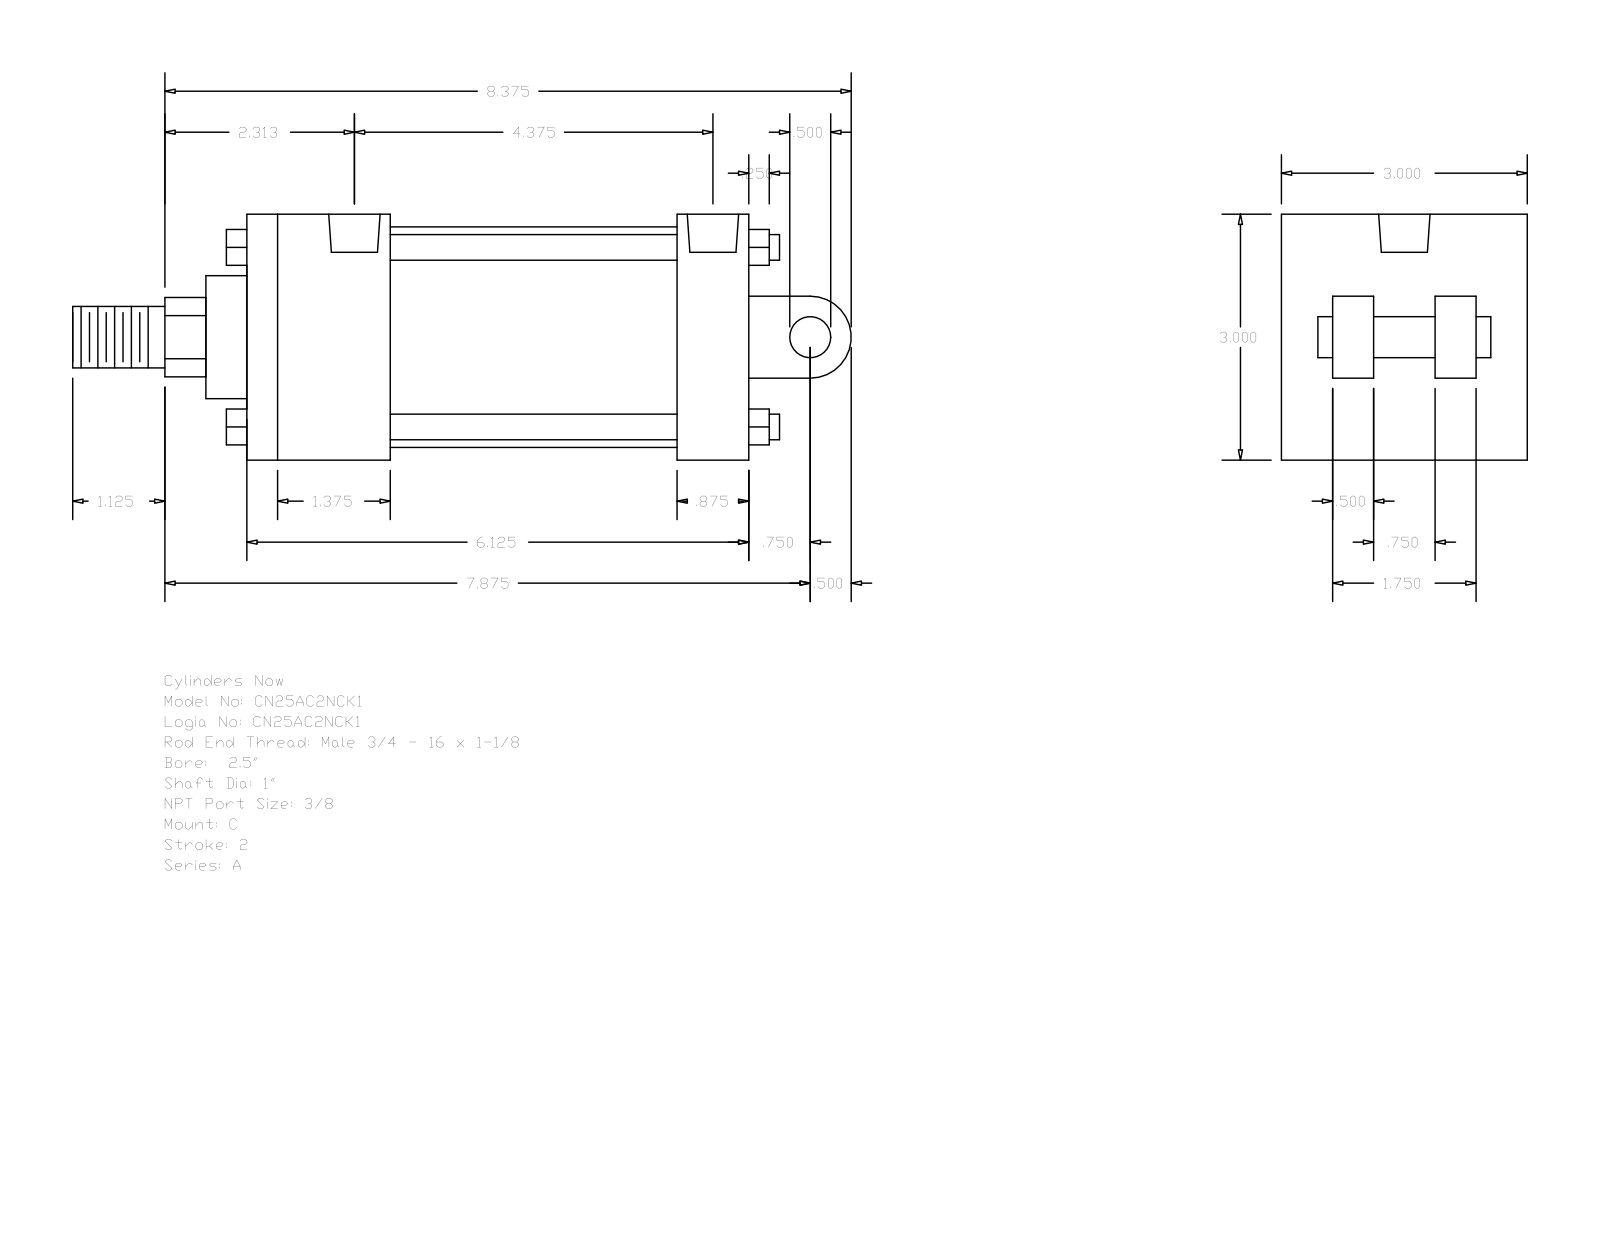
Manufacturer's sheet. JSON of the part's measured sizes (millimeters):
{"part_name": "A_C__0250_1", "step_written_by": "GSSL Pune (CONFIG_CONTROL_DESIGN)", "units": "millimeters", "bodies": {"solids": 0, "faces": 135, "planar": 102, "cylindrical": 33, "other": 0}, "overall_size": [241.3, 76.2, 76.2], "round_holes": [[5.56, 4], [15.93, 2]], "round_bosses_or_shafts": [[7.94, 4], [68.33, 1], [38.1, 1], [25.4, 1], [19.05, 1], [12.7, 1]], "partial_cylinders_radius": [[12.29, 1], [12.7, 1]], "face_to_face_distances": [76.2, 155.57, 12.7, 44.45, 133.35, 88.9, 111.12, 22.22, 15.87, 25.4], "hole_center_spacings": [2.38, 113.5, 115.88, 111.12]}
